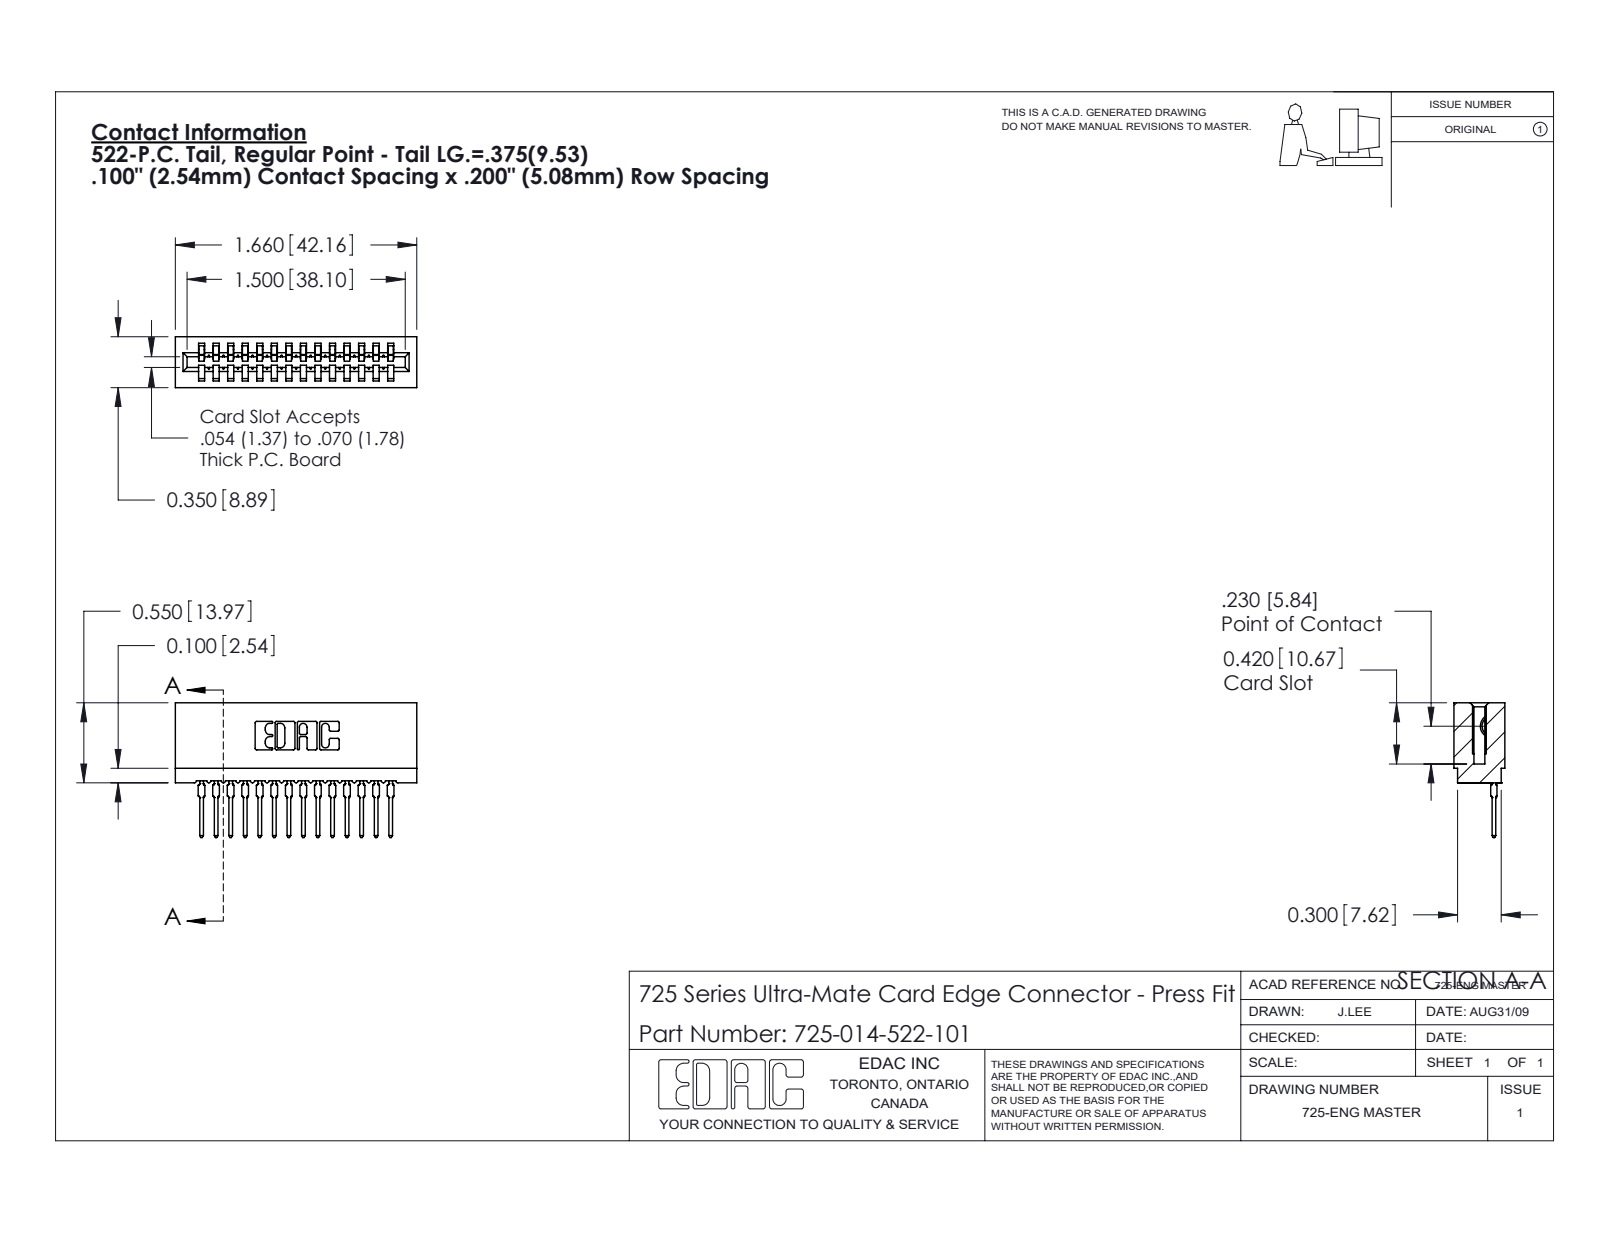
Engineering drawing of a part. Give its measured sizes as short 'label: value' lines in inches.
name: 725-014-522-101; 745-292-001_522; 725 Part_Insulator Option - 01
written by: SolidWorks 2020 (CONFIG_CONTROL_DESIGN)
unit: in
bodies: 15 solids, 1663 faces (993 planar, 306 cylindrical, 364 other)
size: 1.66 × 0.926 × 0.35
volume: 0.205 in³; area: 9.302 in²
rounds: 28× R0.015, 28× R0.021, 22× R0.01, 6× R0.007, 6× R0.031, 4× R0.005, 4× R0.011, 3× R0.026
face distances: 0.1, 0.2, 0.3, 0.4, 0.5, 0.35, 0.6, 0.212, 0.138, 0.7
